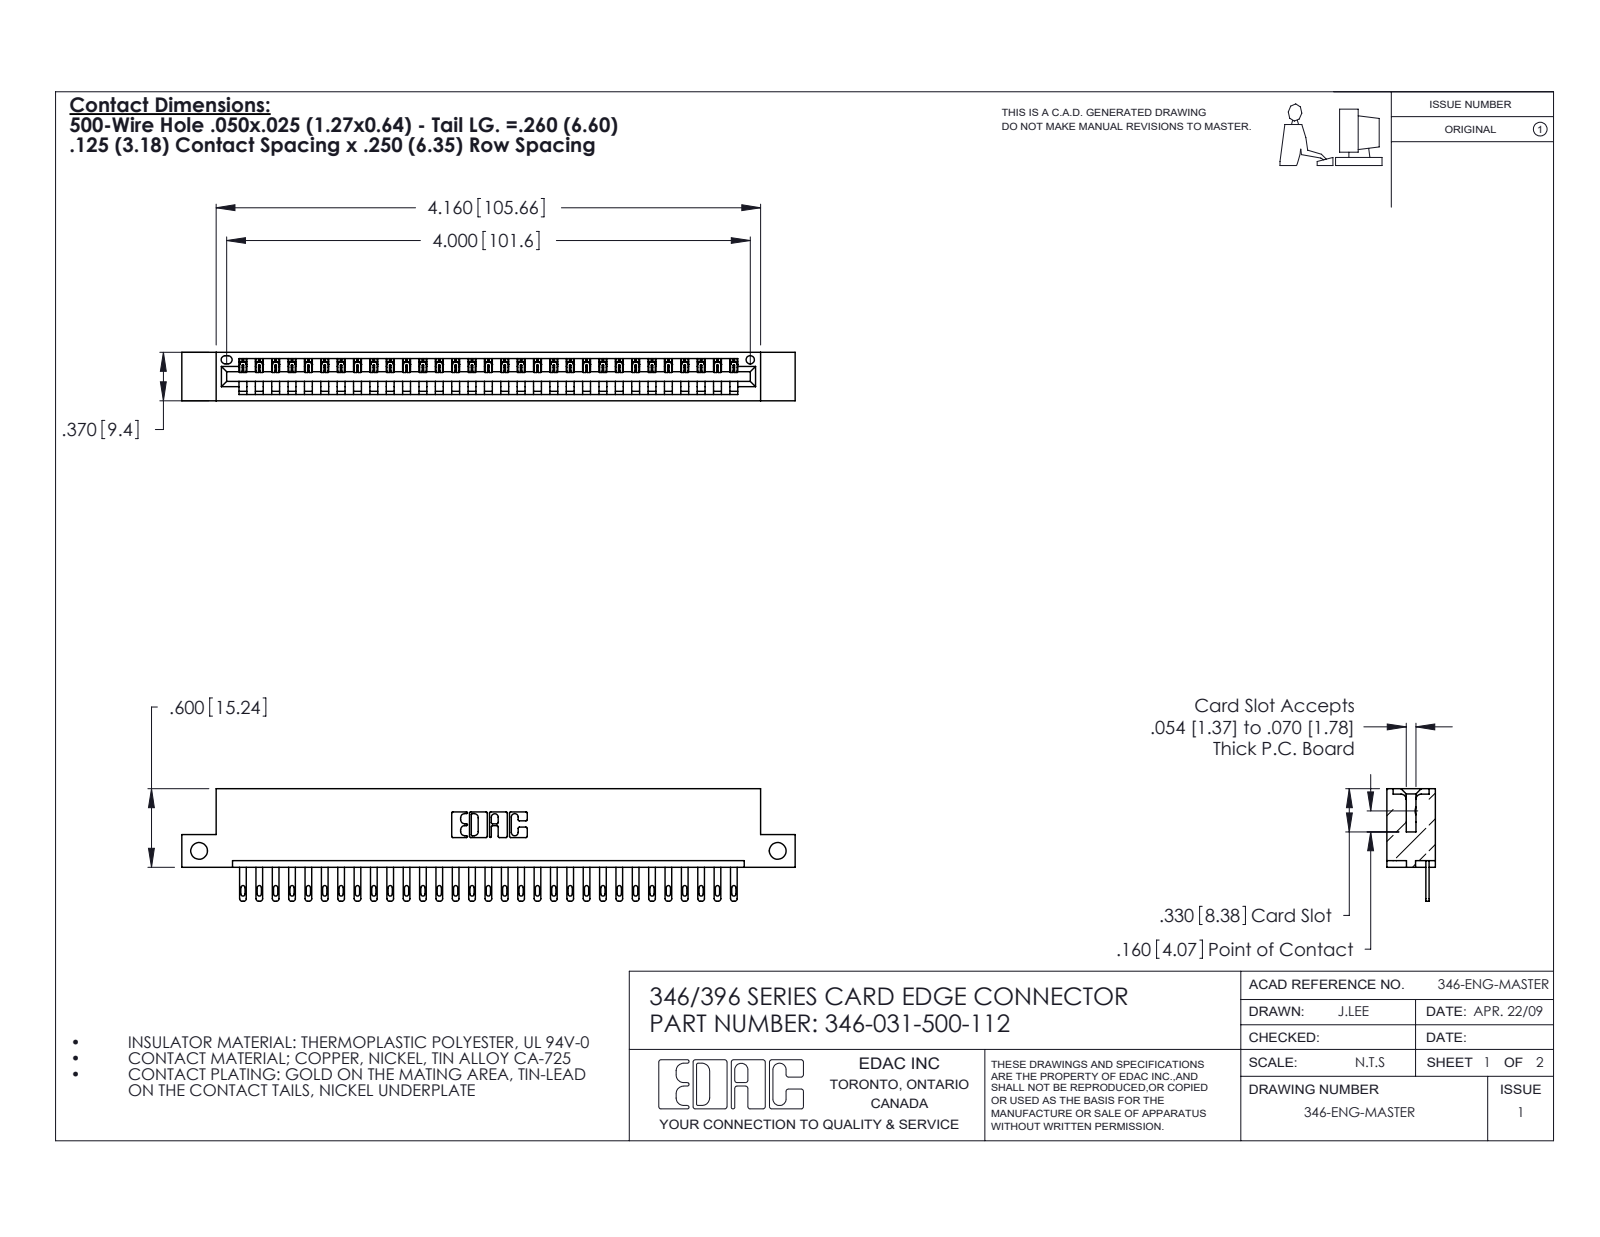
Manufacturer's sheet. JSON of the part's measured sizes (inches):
{"part_name": "345-292-001_345-293-100; 346 Part_Flush Mounting Lugs - Side Mount; 346-031-500-112", "step_written_by": "SolidWorks 2020 (CONFIG_CONTROL_DESIGN)", "units": "inches", "bodies": {"solids": 32, "faces": 1796, "planar": 1130, "cylindrical": 666, "other": 0}, "overall_size": [4.685, 0.86, 0.37], "volume_in3": 0.686, "surface_area_in2": 21.49, "round_holes": [[0.128, 2], [0.064, 1]], "partial_cylinders_radius": [[0.006, 62], [0.016, 62], [0.02, 62], [0.01, 22], [0.007, 6], [0.031, 6], [0.026, 3], [0.031, 2]], "face_to_face_distances": [0.048, 0.322, 0.25, 0.37, 0.072, 0.298, 0.025, 0.148, 0.222, 0.1], "hole_center_spacings": [4.42]}
